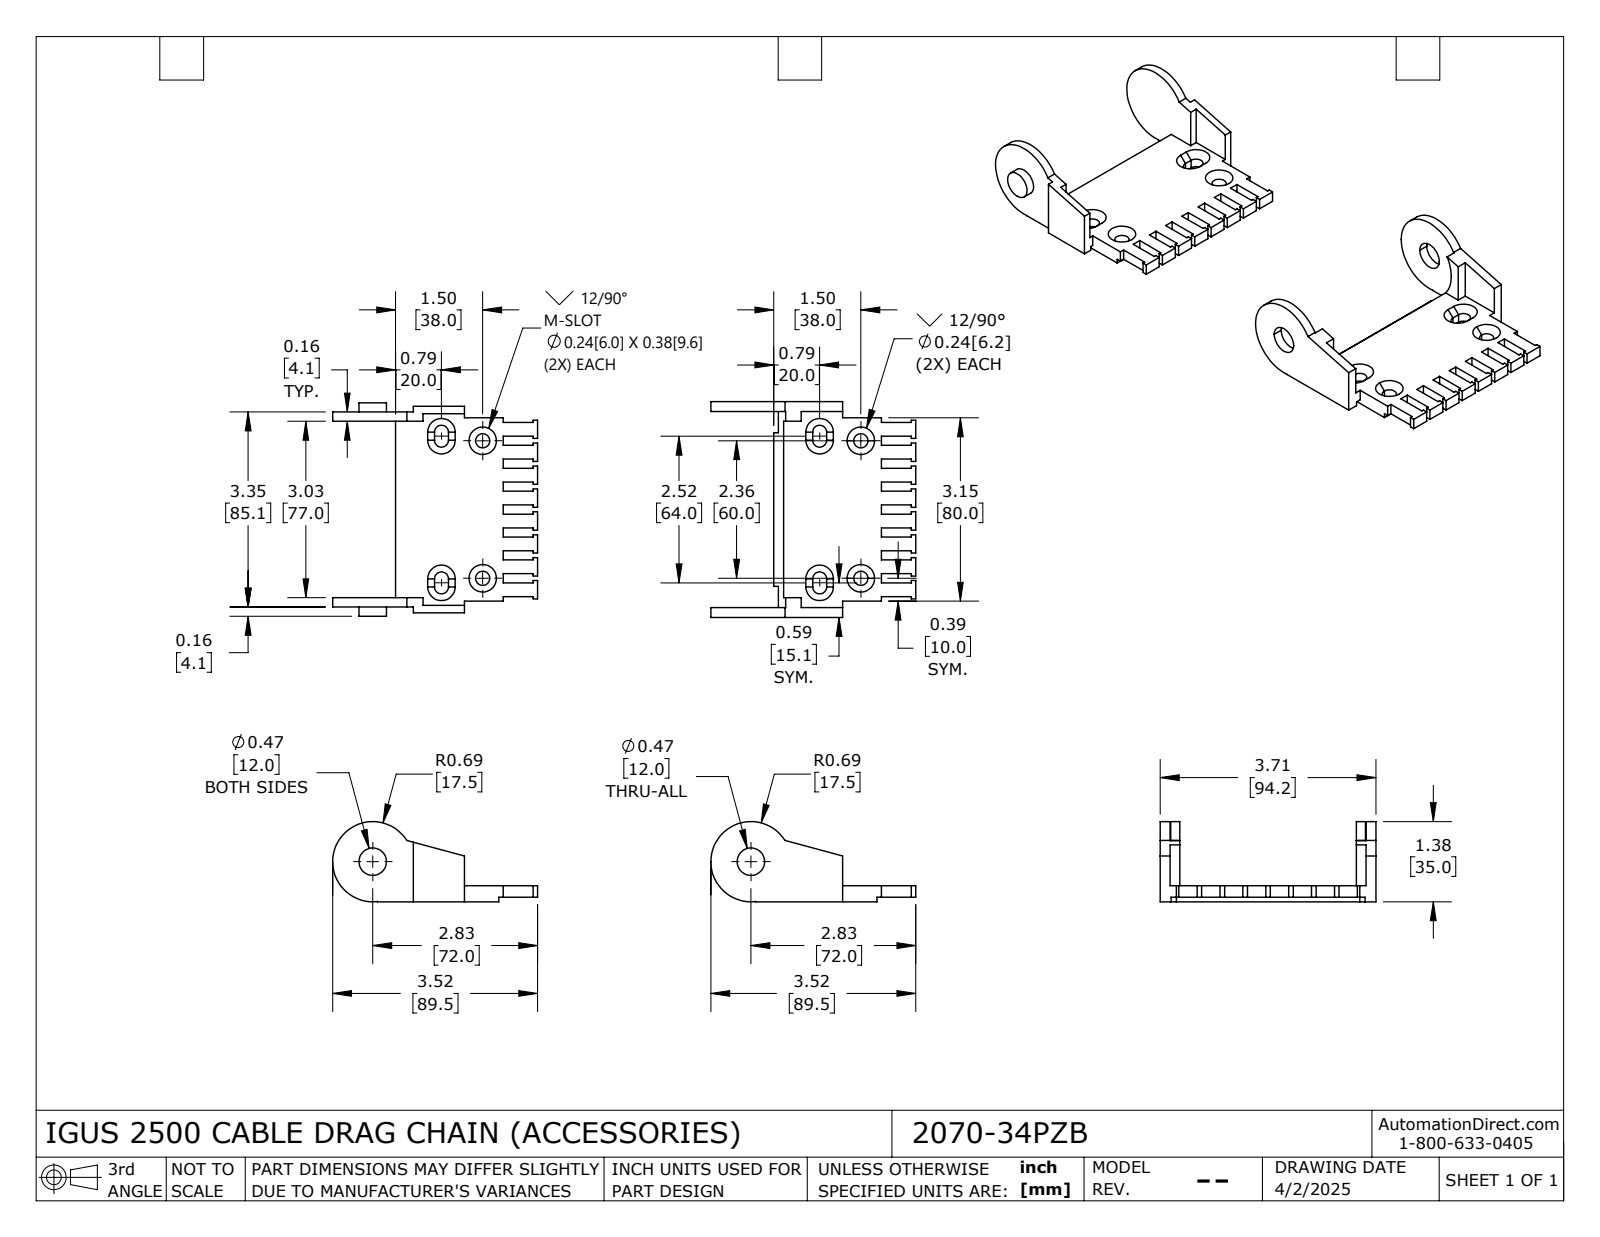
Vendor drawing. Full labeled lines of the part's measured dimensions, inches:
Part name (STEP PRODUCT): 2070-34PZB
STEP written by: SolidWorks 2024 (AUTOMOTIVE_DESIGN)
Units: inches
Bodies: 2 solids, 259 faces (216 planar, 29 cylindrical, 14 other)
Overall size (bounding box): 10.024 × 3.709 × 1.378
Volume: 5.07 in³ · Surface area: 62.71 in²
Round holes (diameter × count): ⌀0.244 ×4, ⌀0.472 ×1
Round bosses / shafts (diameter × count): ⌀0.472 ×1
Partial cylindrical surfaces — rounded edges, fillets, slot ends (radius × count): R0.12 ×8, R0.689 ×2, R0.697 ×1
Main face-to-face distances: 0.276, 0.169, 0.079, 3.37, 0.339, 3.539, 3.201, 0.179, 3.53, 3.36
Hole centre spacings: 2.362, 6.5, 6.916
